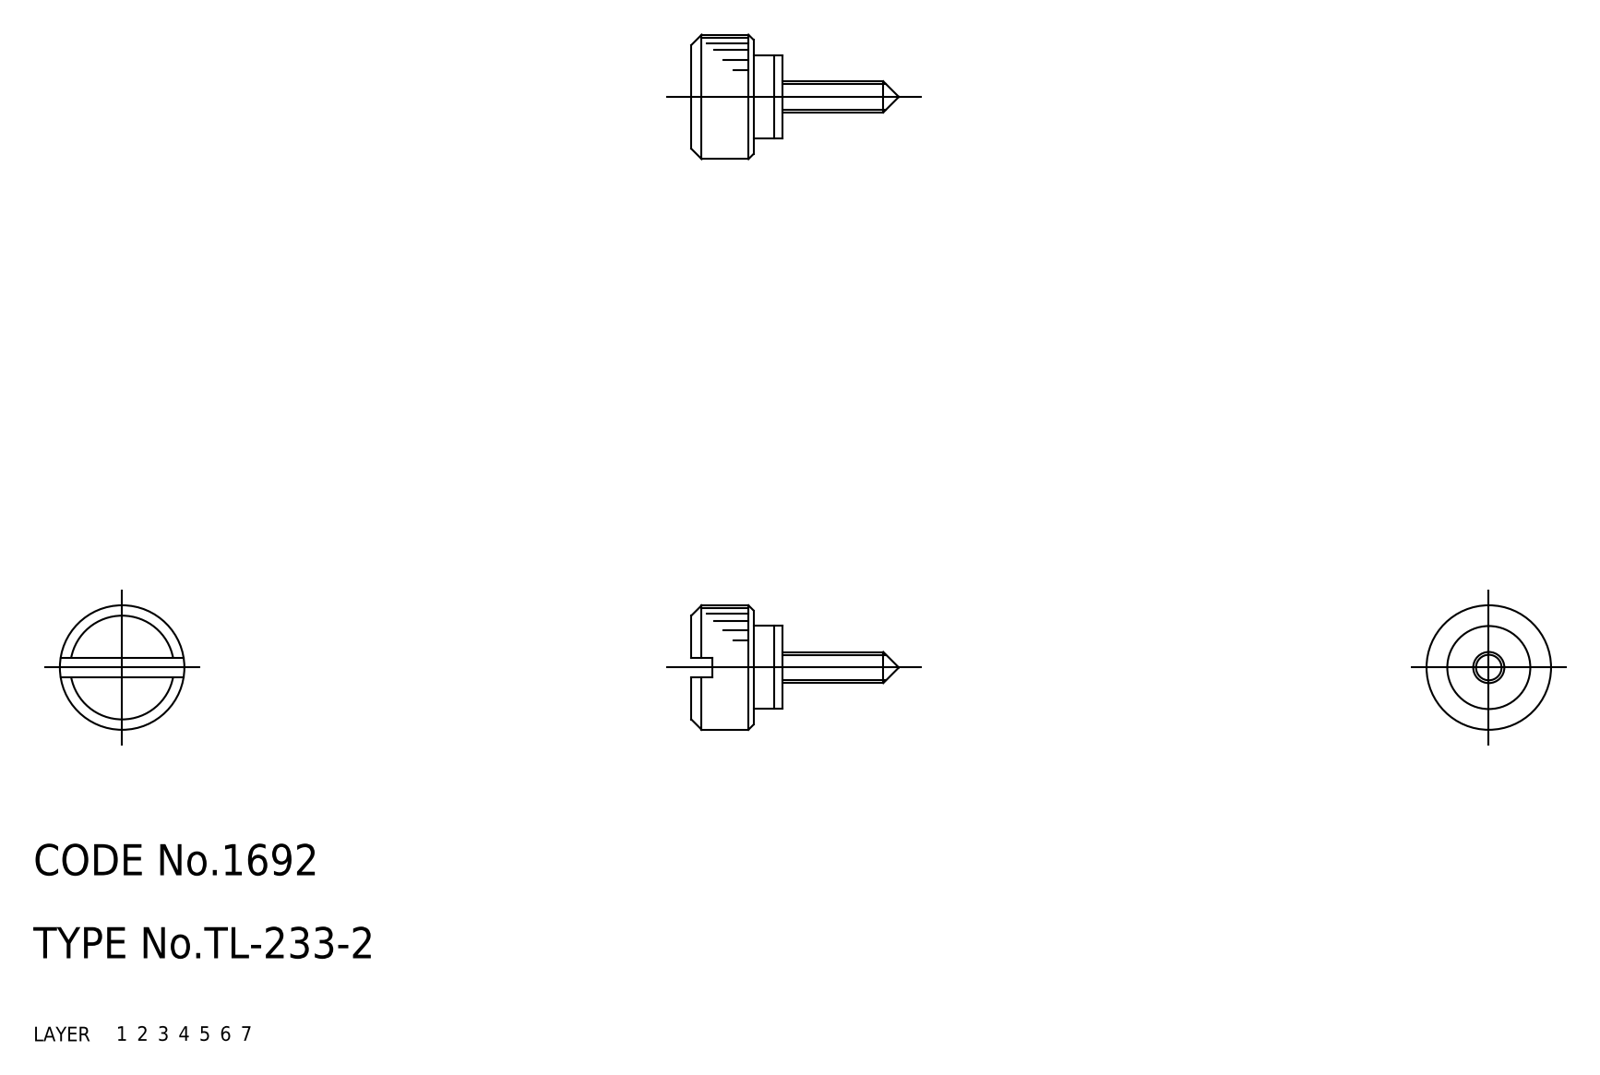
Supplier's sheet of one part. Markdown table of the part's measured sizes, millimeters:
| quantity | value |
| --- | --- |
| part name | washer; knob; TL_233_2_29003_36 |
| STEP written by | CADfix (AUTOMOTIVE_DESIGN) |
| units | millimeters |
| bodies | 2 solids, 37 faces (0 planar, 0 cylindrical, 37 other) |
| overall size | 20 × 12 × 12 |
| volume | 827 mm³ |
| surface area | 717 mm² |
